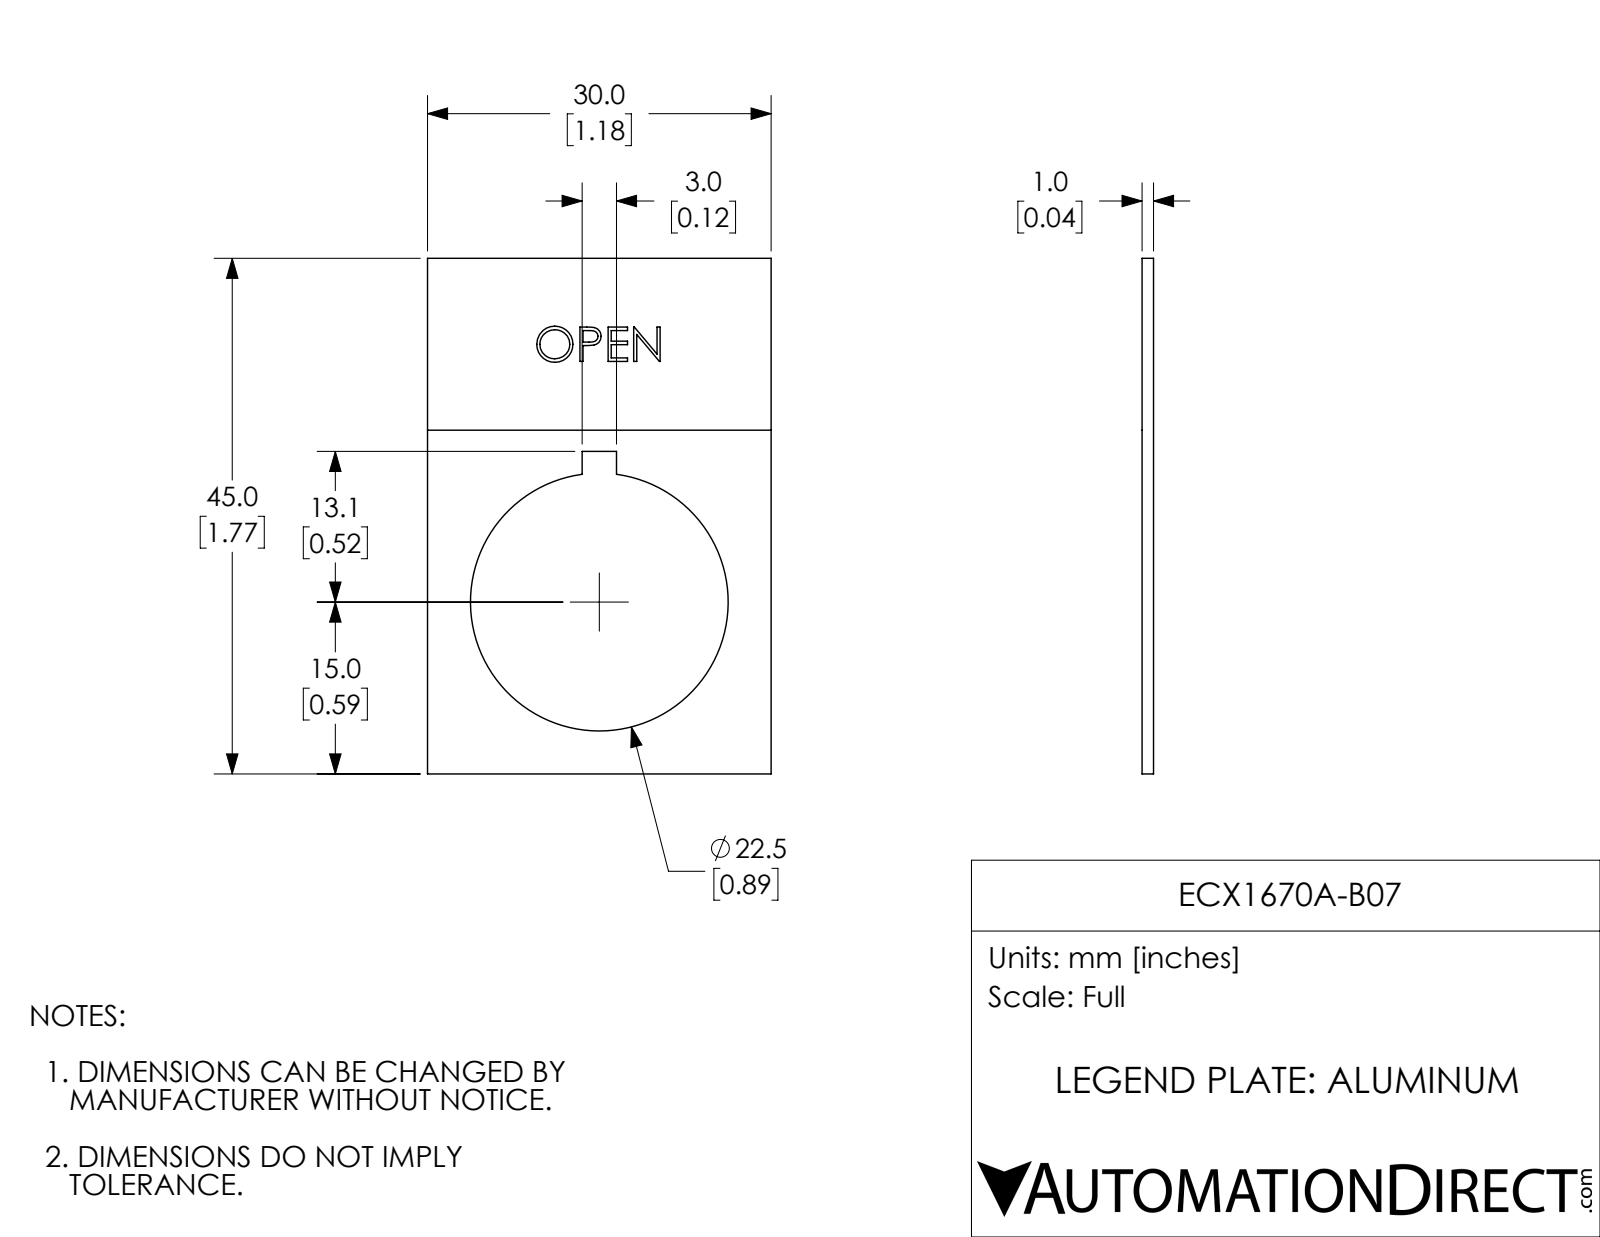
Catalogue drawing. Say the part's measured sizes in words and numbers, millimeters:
The part is named "ECX1670A-B07". Its 3-D file was written by "SolidWorks 2017 (AUTOMOTIVE_DESIGN)". It is 1 solid with 63 faces: 46 planar, 3 cylindrical and 14 other. Overall it measures 45 by 30 by 1 millimeters. Its volume is 950 cubic millimeters and its surface area 2 119 square millimeters. Round holes: 1 of diameter 22.5. The main face-to-face distances are 1, 30, 45, 1, 13.5, 16.5, 28.1, 16.8, 3, 1.8.
